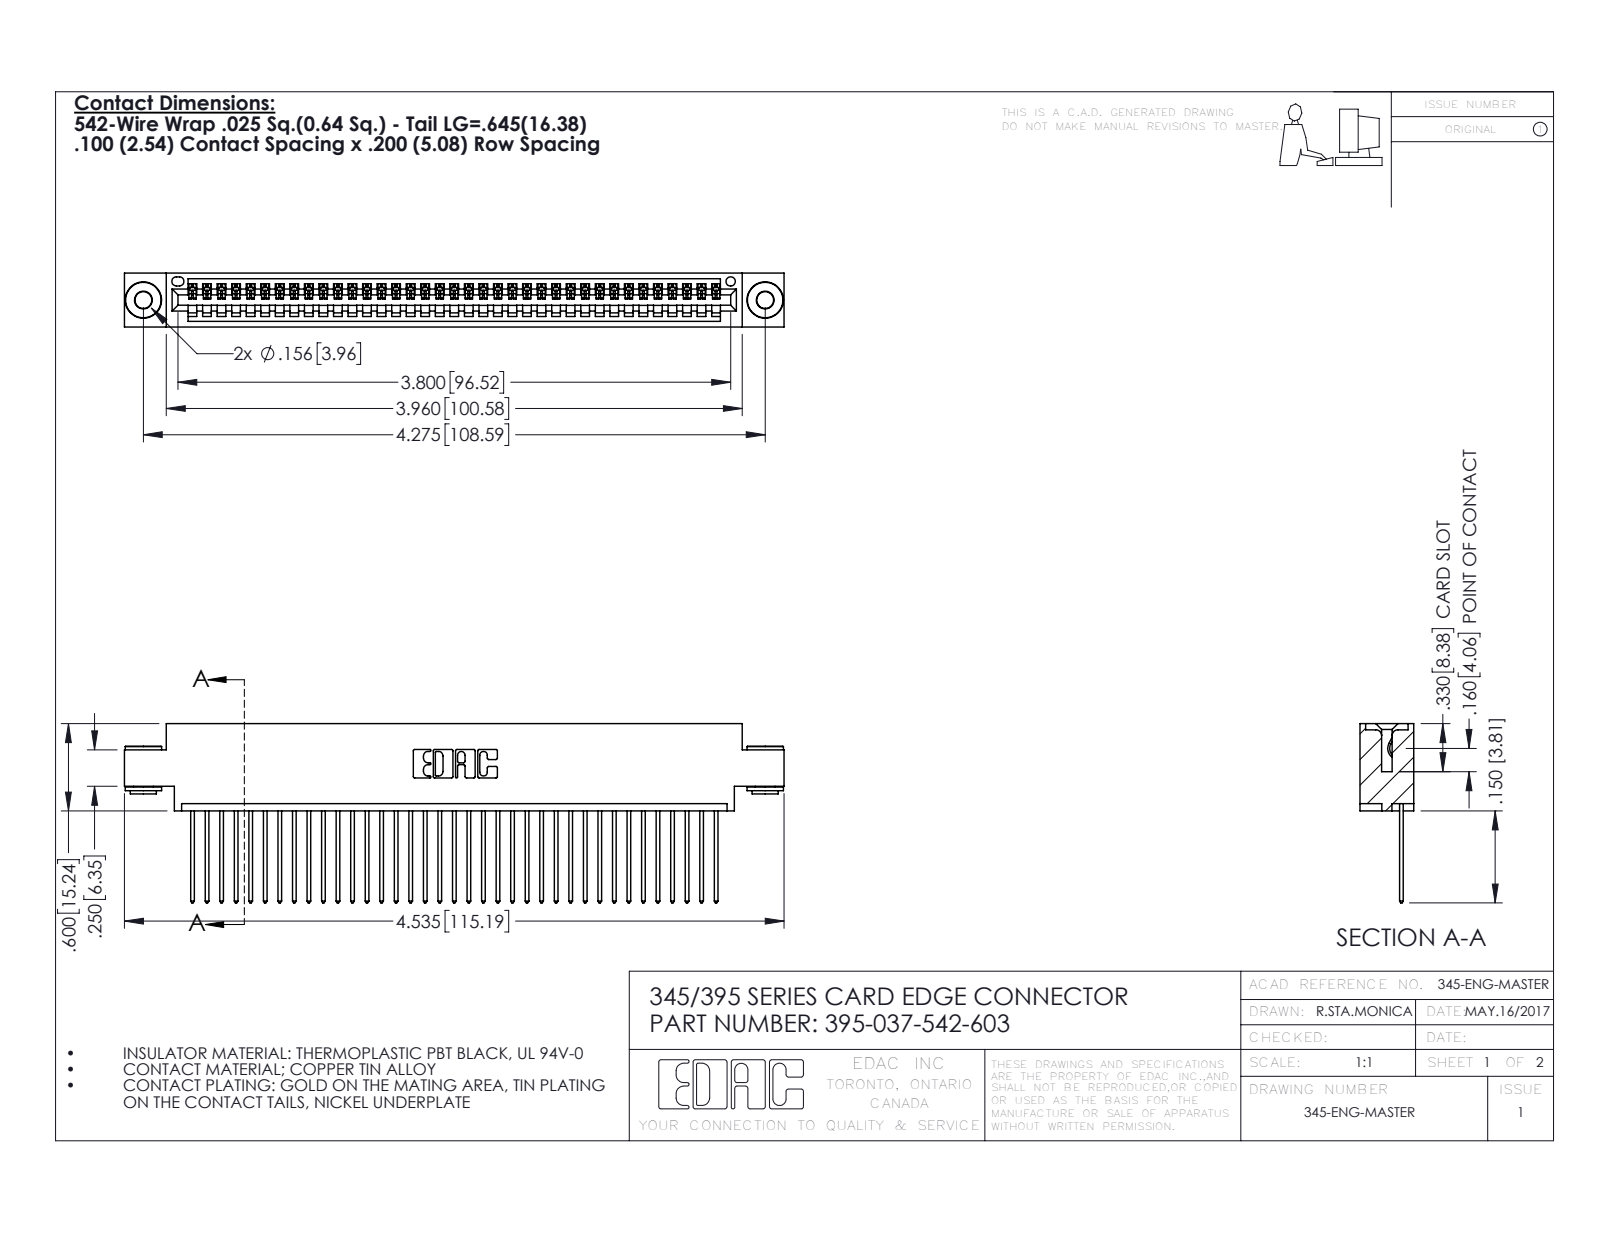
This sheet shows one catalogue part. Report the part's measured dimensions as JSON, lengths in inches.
{"part_name": "345-250-002_345-250-002-102; 345-292-001_345-293-142; 345 Part_0.170 Offset - 0.156 Dia-TH; 395-037-542-603", "step_written_by": "SolidWorks 2016 (CONFIG_CONTROL_DESIGN)", "units": "inches", "bodies": {"solids": 40, "faces": 2314, "planar": 1574, "cylindrical": 732, "other": 8}, "overall_size": [4.535, 1.232, 0.37], "volume_in3": 0.664, "surface_area_in2": 23.66, "round_holes": [[0.116, 2], [0.156, 2], [0.064, 1]], "round_bosses_or_shafts": [[0.25, 2], [0.18, 2], [0.136, 2]], "partial_cylinders_radius": [[0.006, 74], [0.01, 74], [0.01, 22], [0.007, 6], [0.031, 6], [0.026, 3], [0.031, 2], [0.04, 2]], "face_to_face_distances": [0.072, 0.298, 0.37, 0.098, 0.272, 0.025, 0.2, 0.225, 0.175, 0.149], "hole_center_spacings": [0.27, 4.039, 4.275]}
